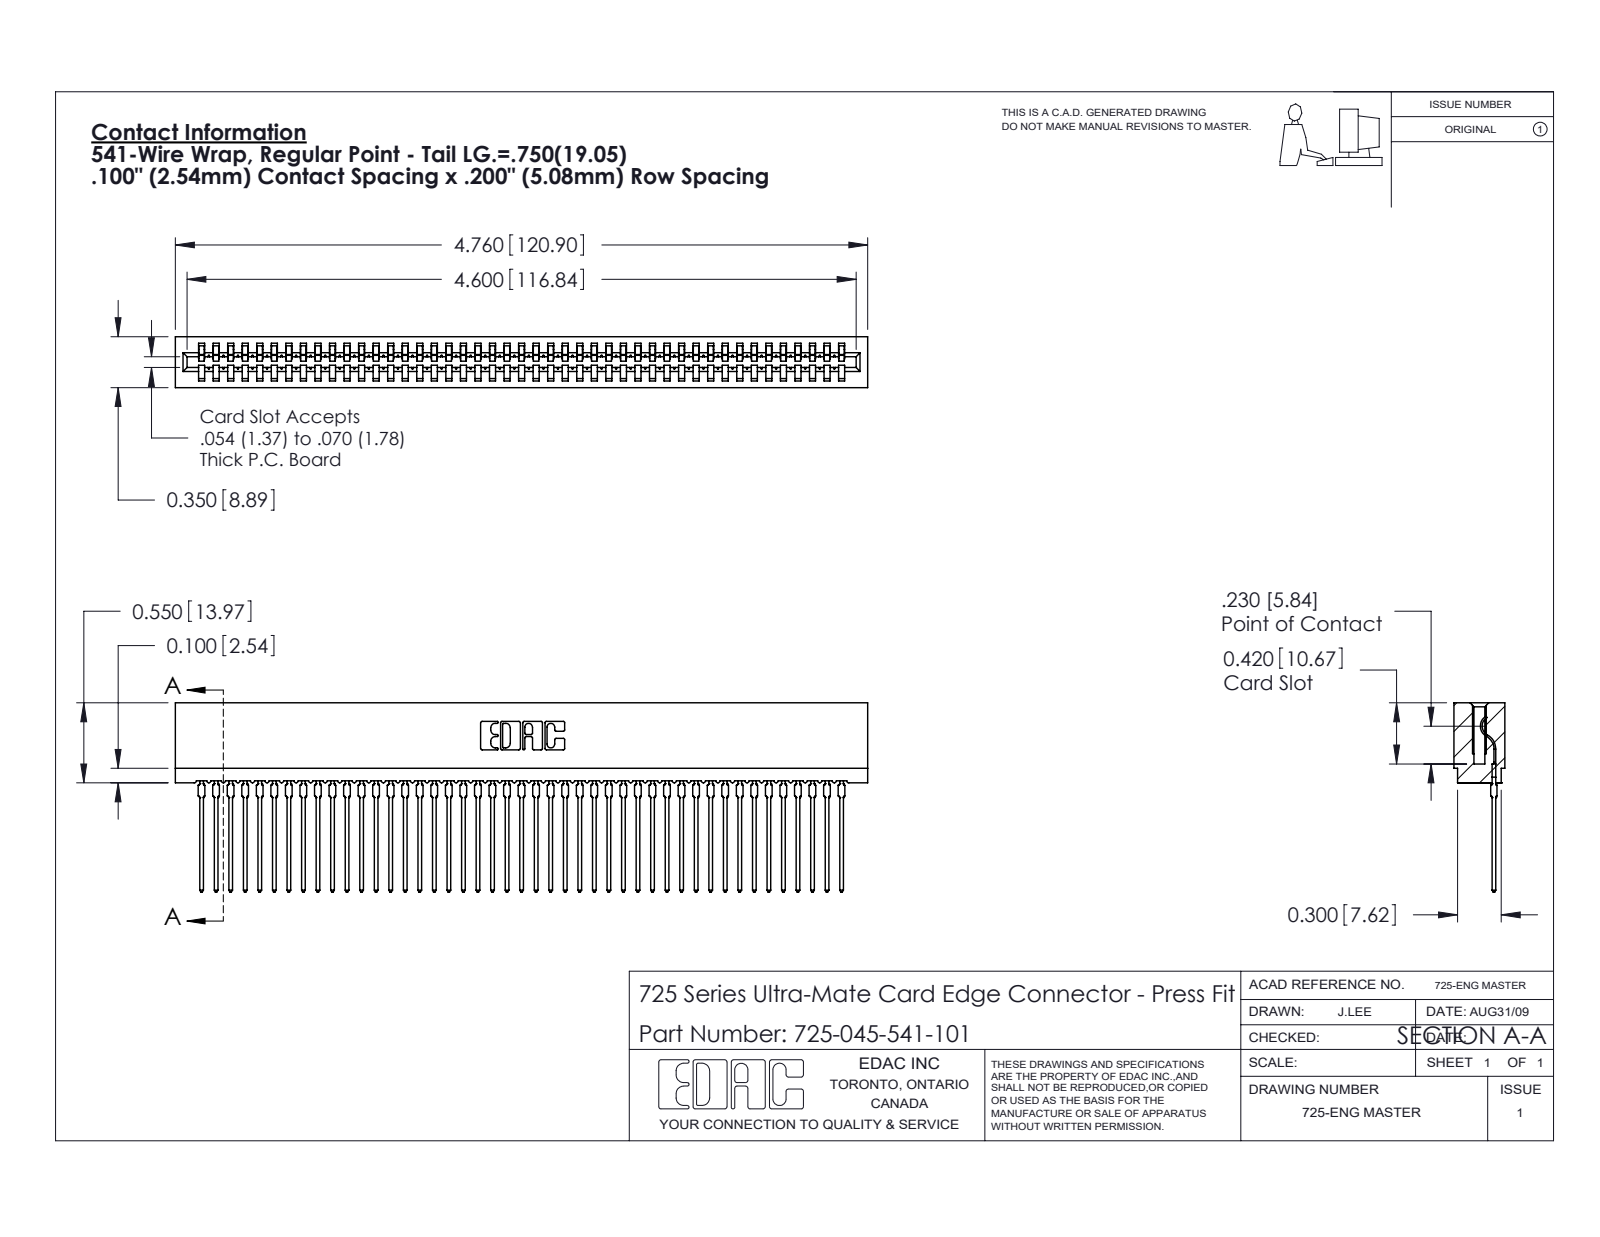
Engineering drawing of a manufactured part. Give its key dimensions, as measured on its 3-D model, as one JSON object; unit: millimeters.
{"part_name": "725 Part_Insulator Option - 01; 745-292-001_541; 725-045-541-101", "step_written_by": "SolidWorks 2020 (CONFIG_CONTROL_DESIGN)", "units": "millimeters", "bodies": {"solids": 46, "faces": 5135, "planar": 3070, "cylindrical": 895, "other": 1170}, "overall_size": [120.9, 33, 8.9], "volume_mm3": 9360, "surface_area_mm2": 18930, "partial_cylinders_radius": [[0.4, 90], [0.5, 90], [0.3, 22], [0.2, 6], [0.8, 6], [0.1, 4], [0.3, 4], [0.7, 3]], "face_to_face_distances": [8.9, 1.6, 7.3, 5.1, 5.4, 3.5, 2.5, 1.1, 7.7, 2.4]}
